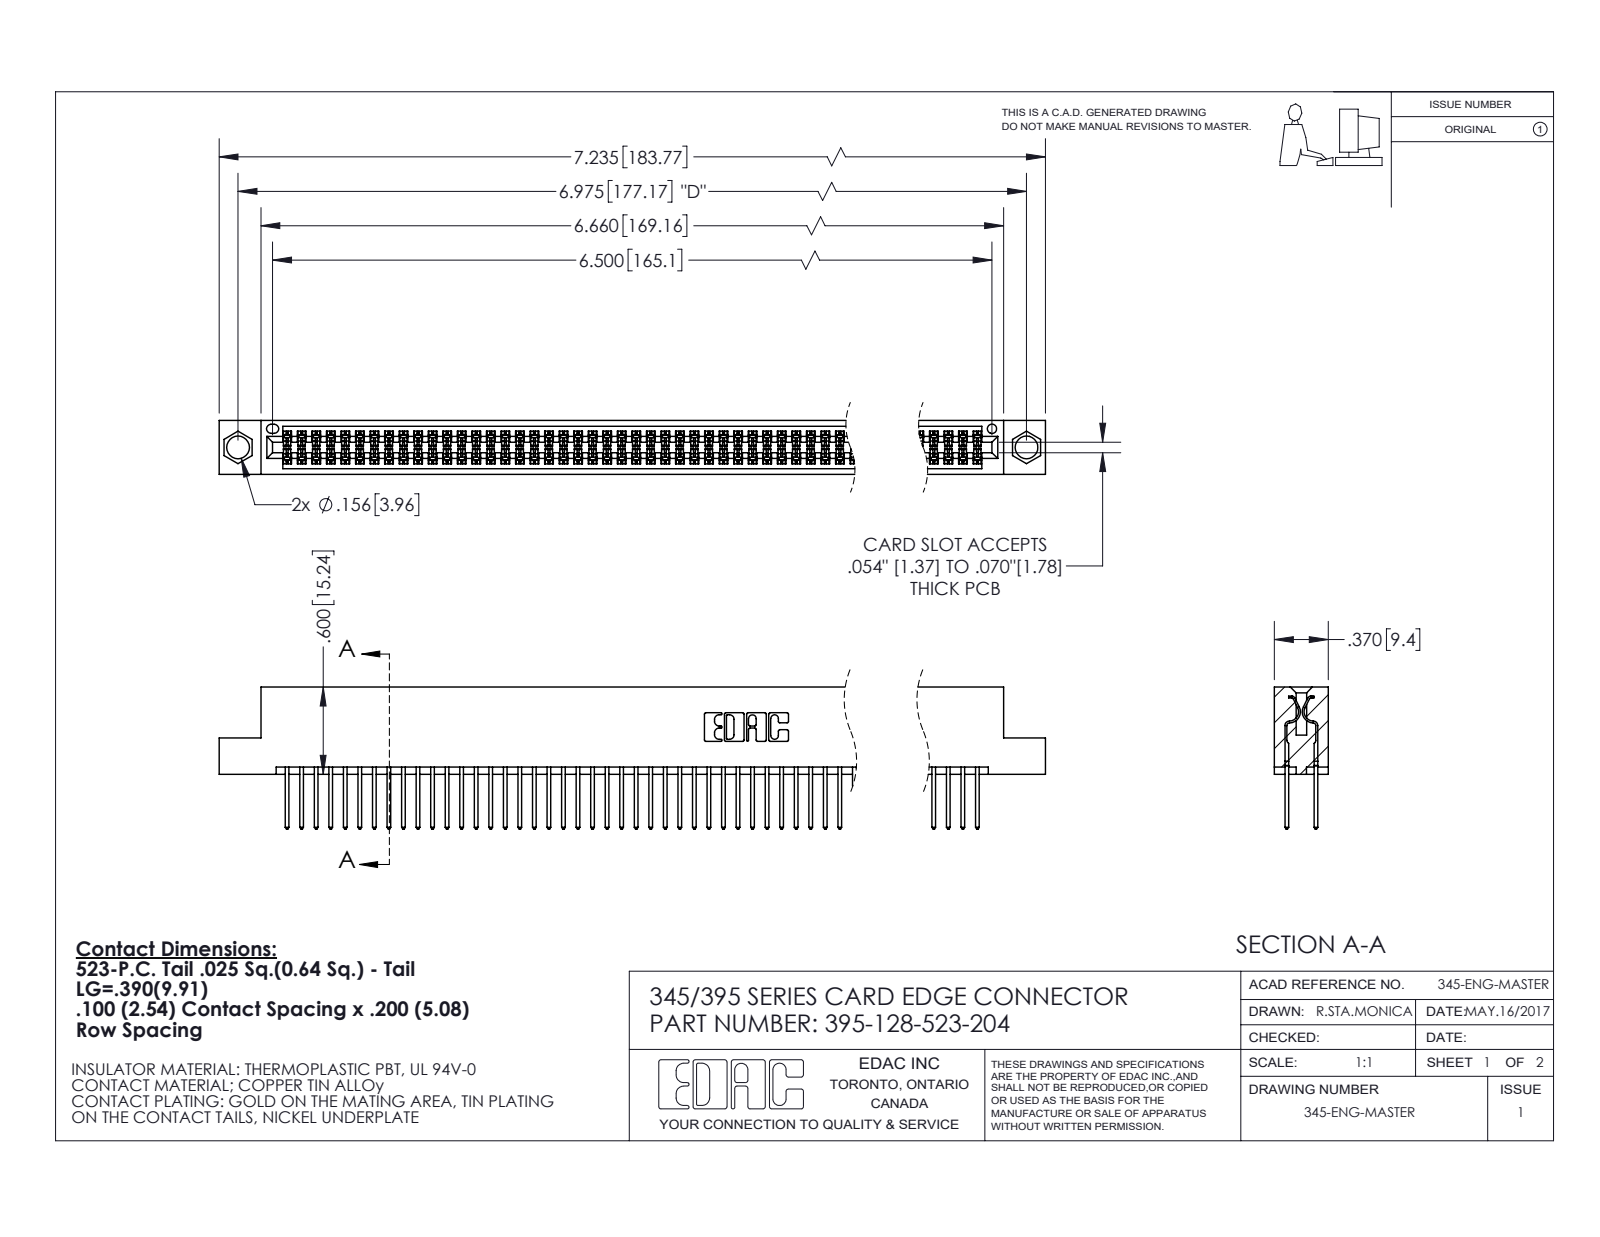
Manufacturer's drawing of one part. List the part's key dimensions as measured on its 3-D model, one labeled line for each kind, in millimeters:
Part name (STEP PRODUCT): 395-128-523-204; 345 Part_Flush Mounting Lugs - 0.156 Dia-TI; 345-292-001_345-293-123
STEP written by: SolidWorks 2020 (CONFIG_CONTROL_DESIGN)
Units: millimetres
Bodies: 129 solids, 6540 faces (4318 planar, 2222 cylindrical, 0 other)
Overall size (bounding box): 183.8 × 24.8 × 9.4
Volume: 18 210 mm³ · Surface area: 28 370 mm²
Round holes (diameter × count): ⌀4 ×2, ⌀1.6 ×1
Partial cylindrical surfaces — rounded edges, fillets, slot ends (radius × count): R0.2 ×192, R0.3 ×128, R0.3 ×22, R0.2 ×6, R0.8 ×6, R0.7 ×3, R0.4 ×2, R0.5 ×2
Main face-to-face distances: 7.6, 1.8, 5.1, 2.5, 6.9, 0.6, 9.4, 5.7, 4.4, 3.8
Hole centre spacings: 6.9, 171.2, 177.2
